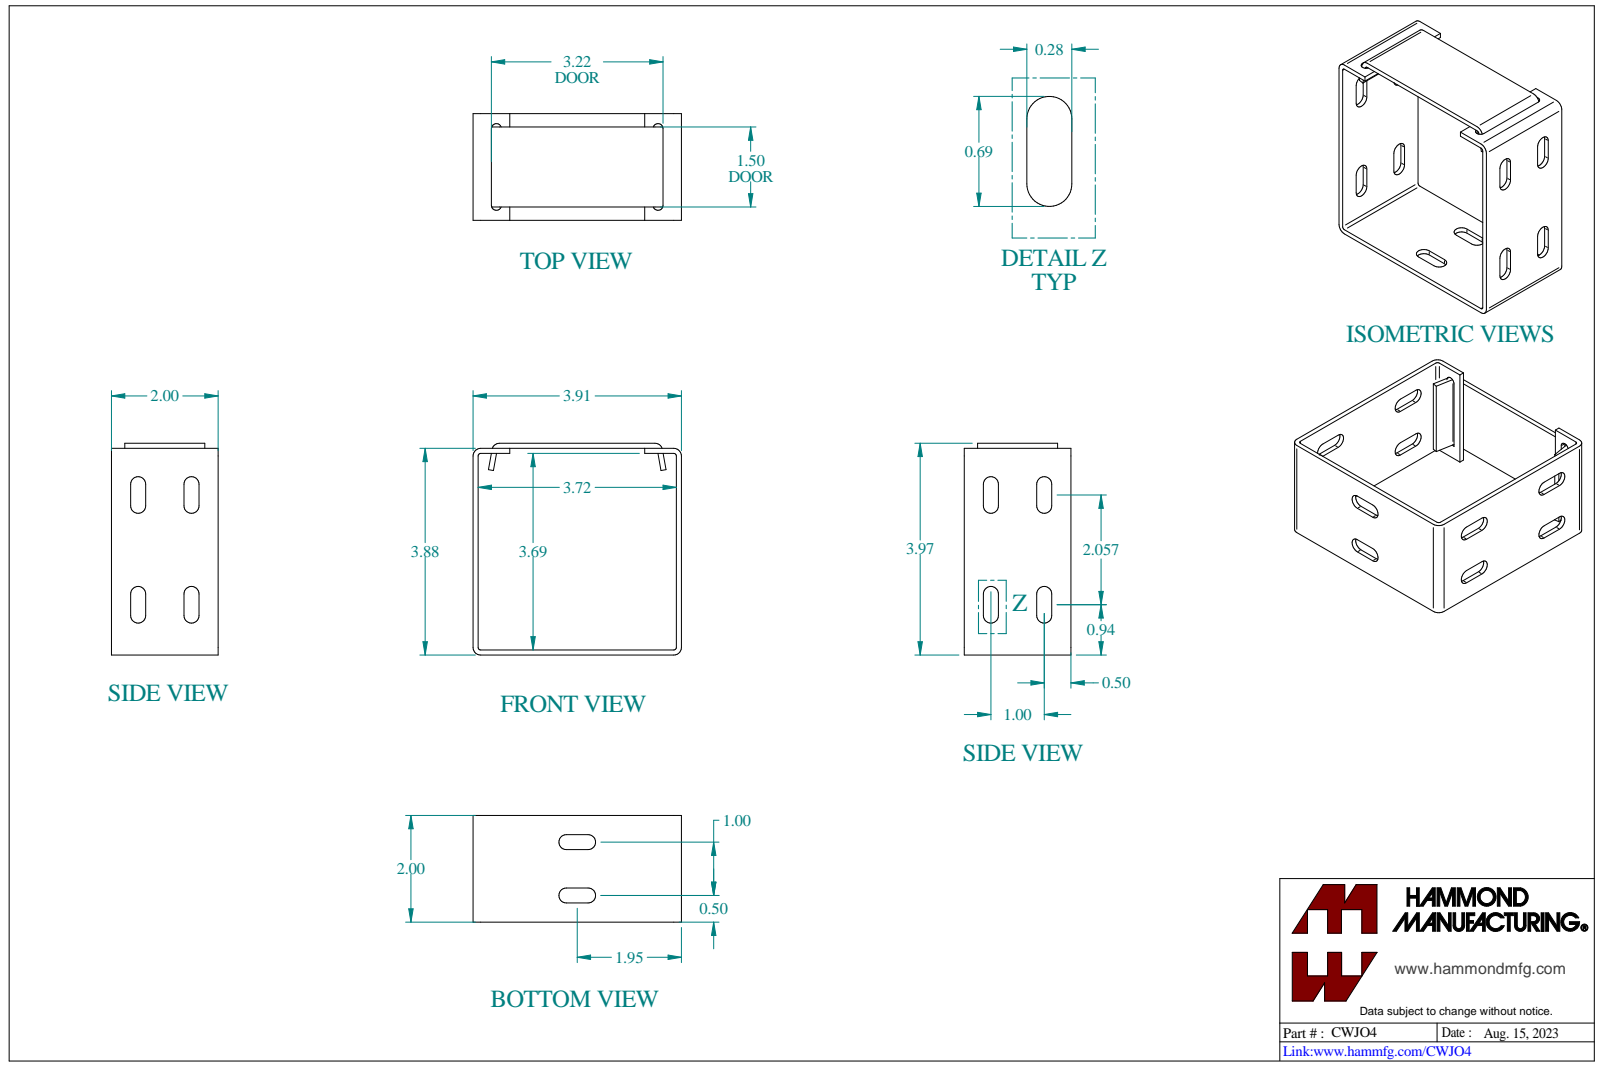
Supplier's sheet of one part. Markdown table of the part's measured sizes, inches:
| quantity | value |
| --- | --- |
| part name | CWJO4 |
| STEP written by | SolidWorks 2023 (CONFIG_CONTROL_DESIGN) |
| units | inches |
| bodies | 2 solids, 94 faces (48 planar, 46 cylindrical, 0 other) |
| overall size | 3.97 × 3.906 × 2 |
| volume | 2.711 in³ |
| surface area | 63.13 in² |
| partial cylindrical surfaces (radius × count) | 0.141 × 8, 0.048 × 6, 0.143 × 6, 0.094 × 4, 0.141 × 4 |
| main face-to-face distances | 0.095, 3.811, 0.095, 3.78, 3.906, 3.716, 3.875, 3.97, 3.875, 3.685 |
